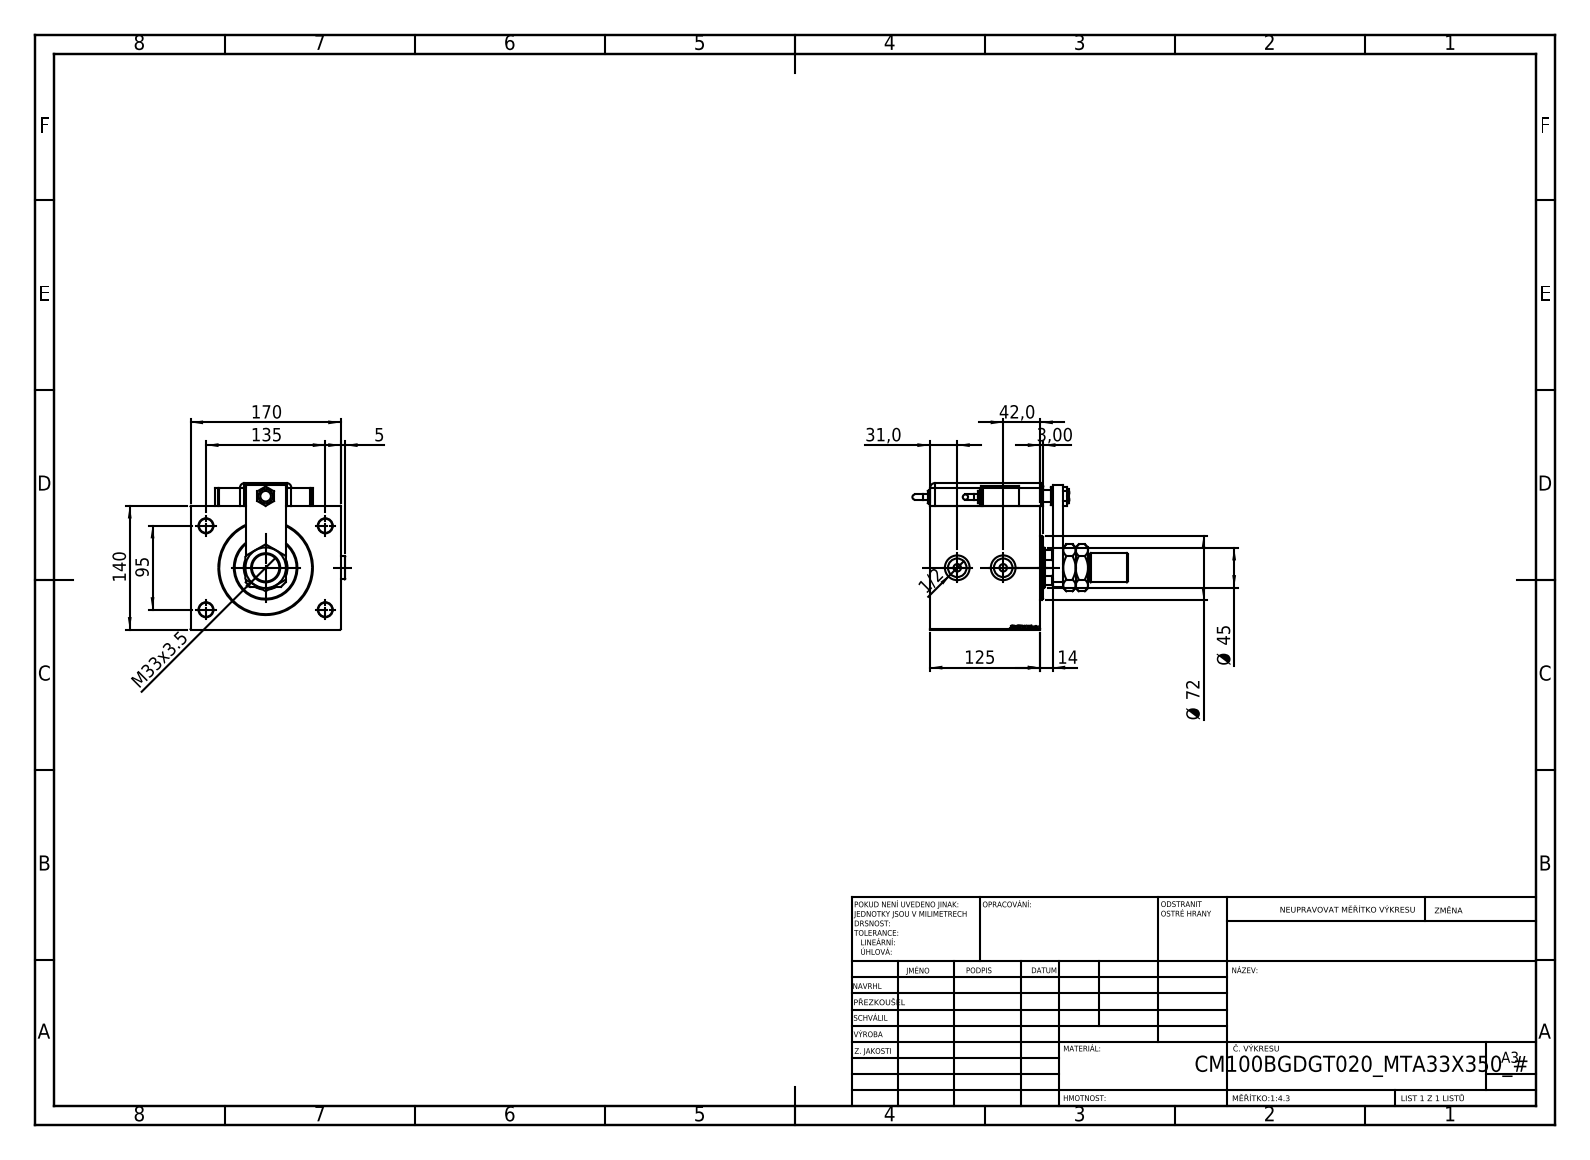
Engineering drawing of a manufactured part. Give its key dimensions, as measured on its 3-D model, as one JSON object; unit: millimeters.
{"part_name": "V450CM_B_VCP; Q_T_W_MTA; SWITCH_Q_FRONT_BACK; SWITCH Q (+7 more)", "step_written_by": "SolidWorks 2019 (CONFIG_CONTROL_DESIGN)", "units": "millimeters", "bodies": {"solids": 16, "faces": 1369, "planar": 657, "cylindrical": 129, "other": 583}, "overall_size": [243.76, 174.9, 165.8], "volume_mm3": 3111000, "surface_area_mm2": 302771, "round_holes": [[16, 4], [4, 2], [8, 2], [8.5, 2], [20.96, 2], [28, 2], [12, 1], [13, 1], [14, 1], [31.5, 1], [33, 1], [45, 1]], "round_bosses_or_shafts": [[20, 3], [26, 2], [16, 2], [14, 2], [6, 2], [72, 1], [31, 1]], "partial_cylinders_radius": [[5, 9], [10, 1], [22, 1]], "face_to_face_distances": [140, 125, 51, 170, 74, 3, 10, 77, 21.6, 29.4], "hole_center_spacings": [82.54, 75.36, 95, 135, 145.15, 165.08, 20, 52]}
